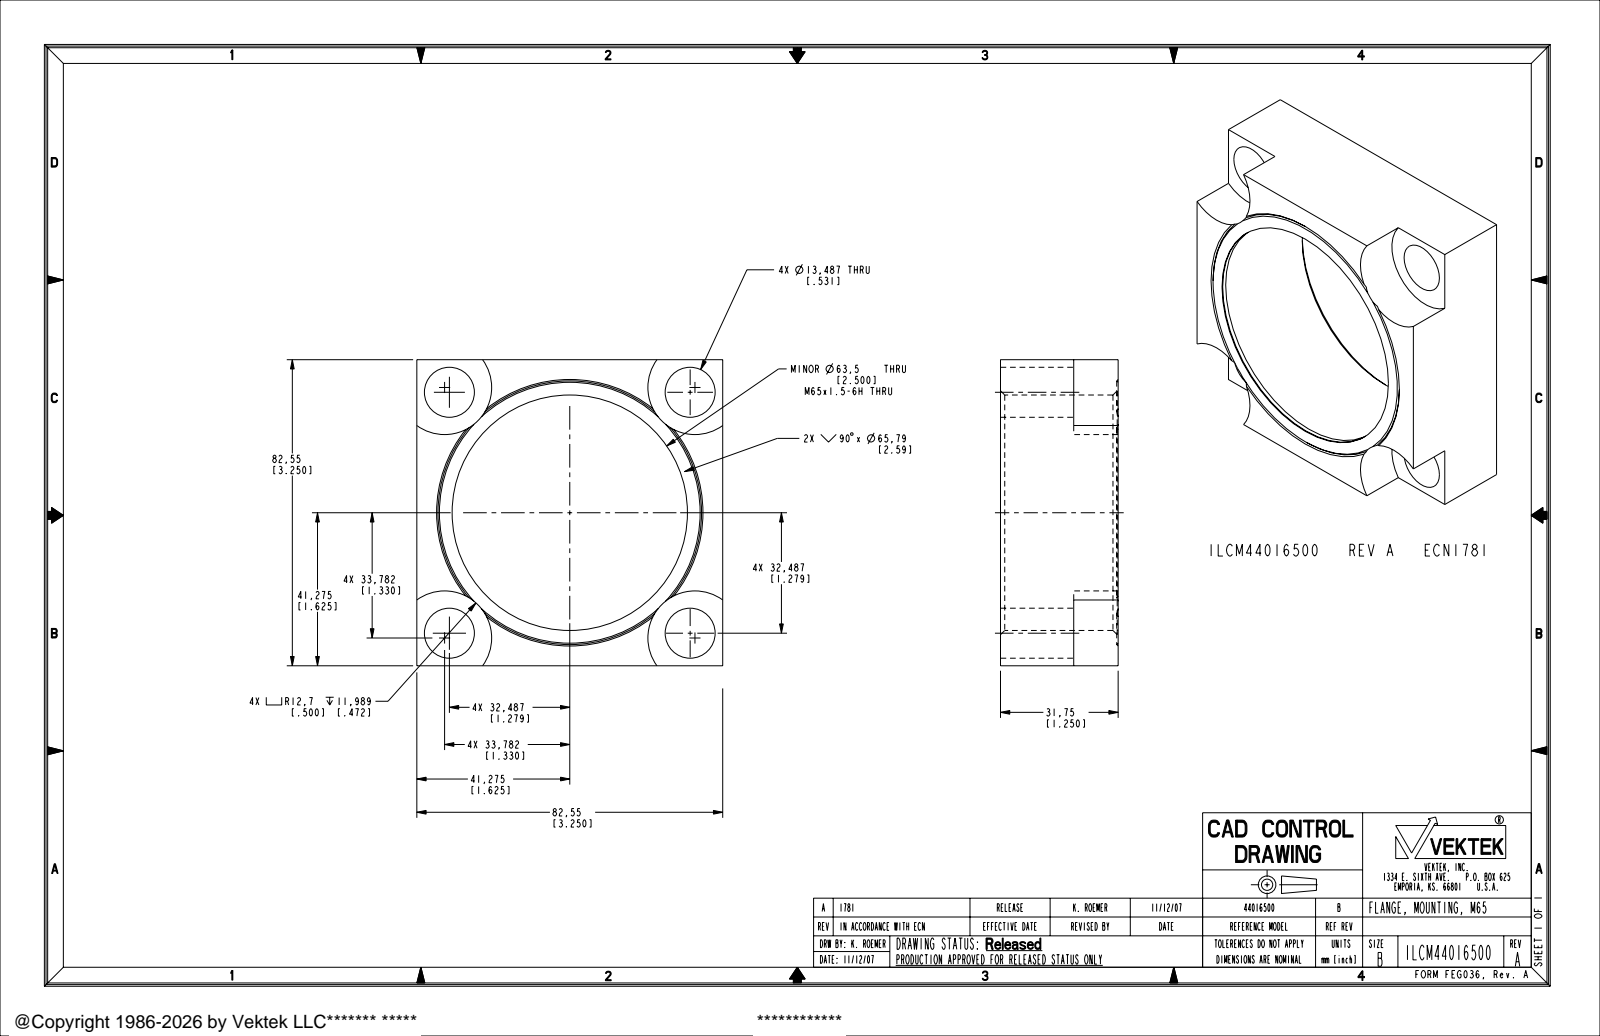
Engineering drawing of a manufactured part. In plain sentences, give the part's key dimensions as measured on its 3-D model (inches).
The part is named "ILCM44016500". Its 3-D file was written by "PRO/ENGINEER BY PARAMETRIC TECHNOLOGY CORPORATION, 2005180 (AUTOMOTIVE_DESIGN_CC2)". It is 1 solid with 43 faces: 15 planar, 16 cylindrical and 12 other. Overall it measures 3.25 by 3.25 by 1.25 inches. Its volume is 5.302 cubic inches and its surface area 41.23 square inches. Round holes: 4 of diameter 0.531, 1 of diameter 2.5. Partial cylindrical surfaces (rounded edges, fillets, slot ends): 4 of radius 0.5. The main face-to-face distances are 3.25, 1.25, 0.472, 0.778, 0.462, 1.24. The hole center spacings are 1.809, 2.558, 3.618.
